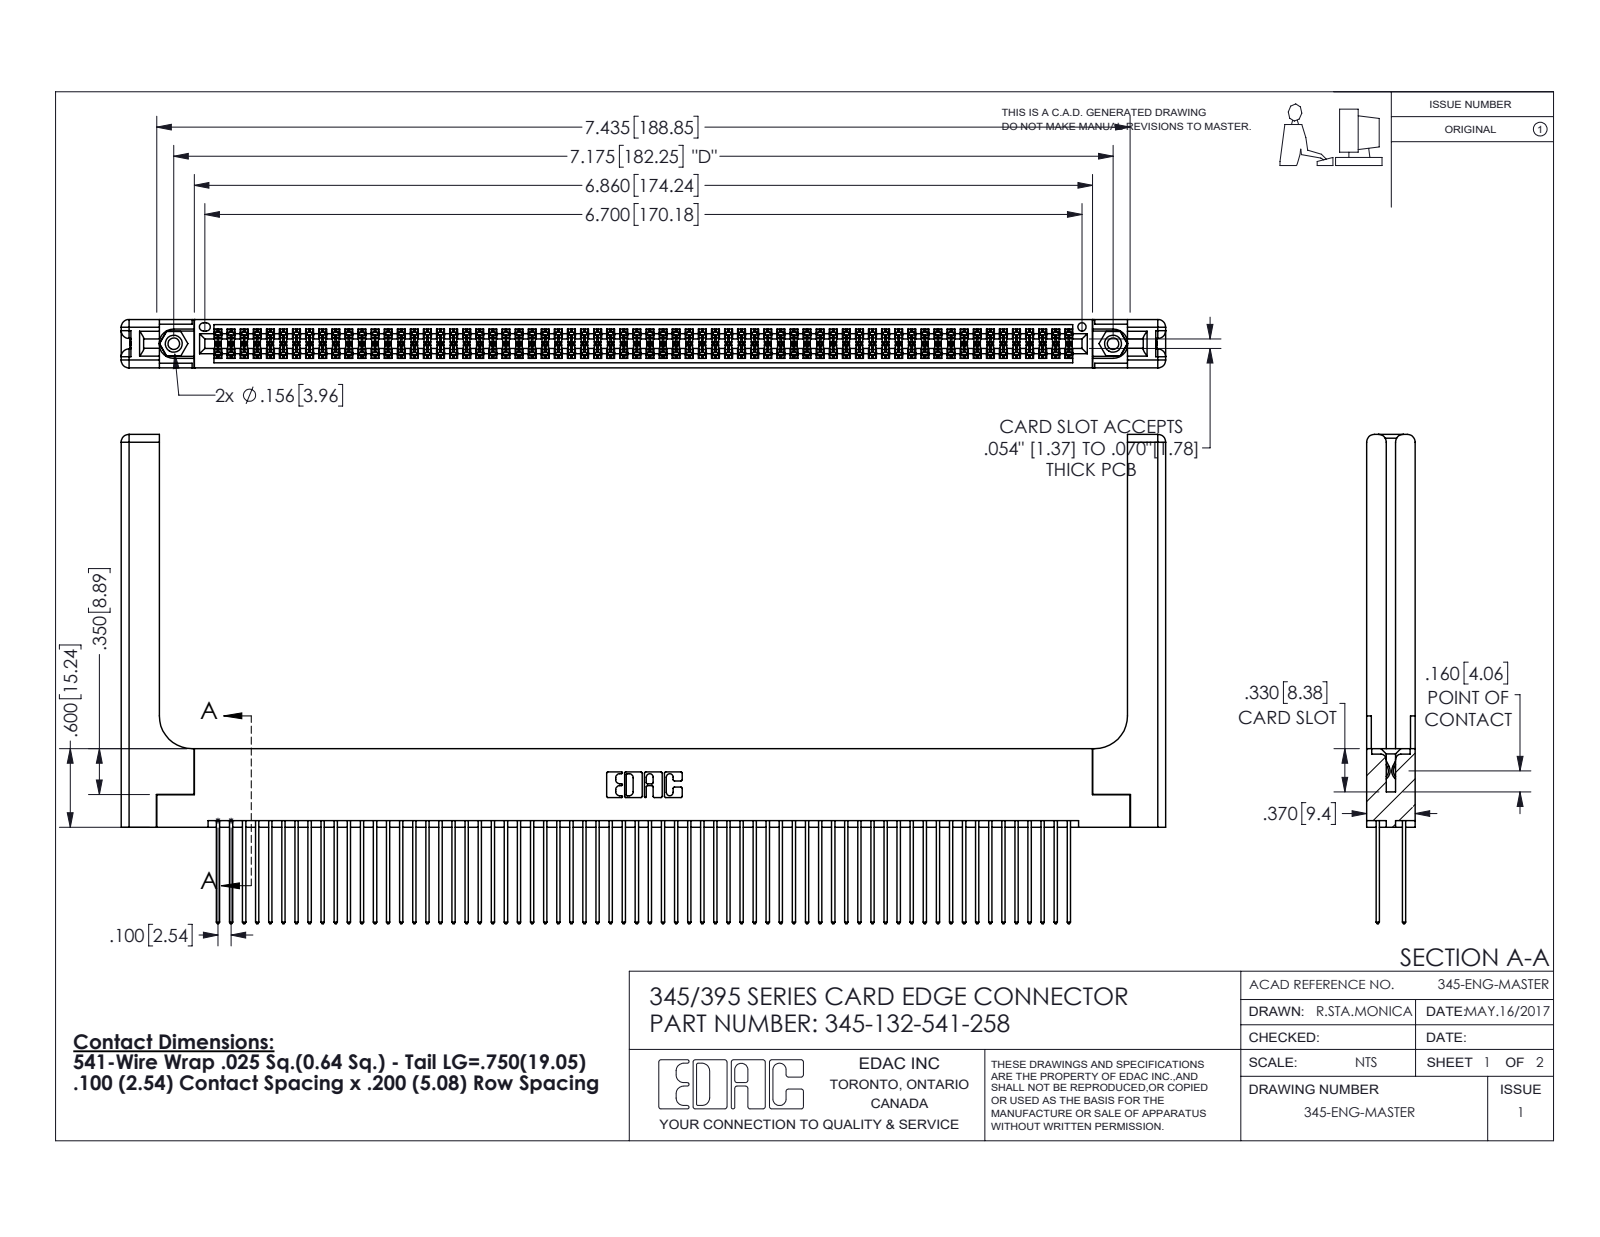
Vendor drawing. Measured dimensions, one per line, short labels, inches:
name: 345 Part_Flush Mounting Lugs - 0.156 Dia-TH; 345-220-058_345-220-058; 345-292-001_345-293-141; 345-250-001_345-250-001-102 (+1 more)
written by: SolidWorks 2016 (CONFIG_CONTROL_DESIGN)
unit: in
bodies: 137 solids, 6982 faces (4584 planar, 2338 cylindrical, 60 other)
size: 7.979 × 3.737 × 0.37
volume: 1.778 in³; area: 61.43 in²
holes: 2× ⌀0.089, 2× ⌀0.125, 2× ⌀0.156, 1× ⌀0.064
bosses: 2× ⌀0.155
rounds: 198× R0.006, 132× R0.01, 22× R0.01, 16× R0.06, 6× R0.007, 6× R0.031, 3× R0.026, 2× R0.014
face distances: 0.072, 0.298, 0.2, 0.098, 0.272, 0.025, 0.37, 0.225, 0.175, 0.148
hole spacings: 0.27, 6.939, 7.175
